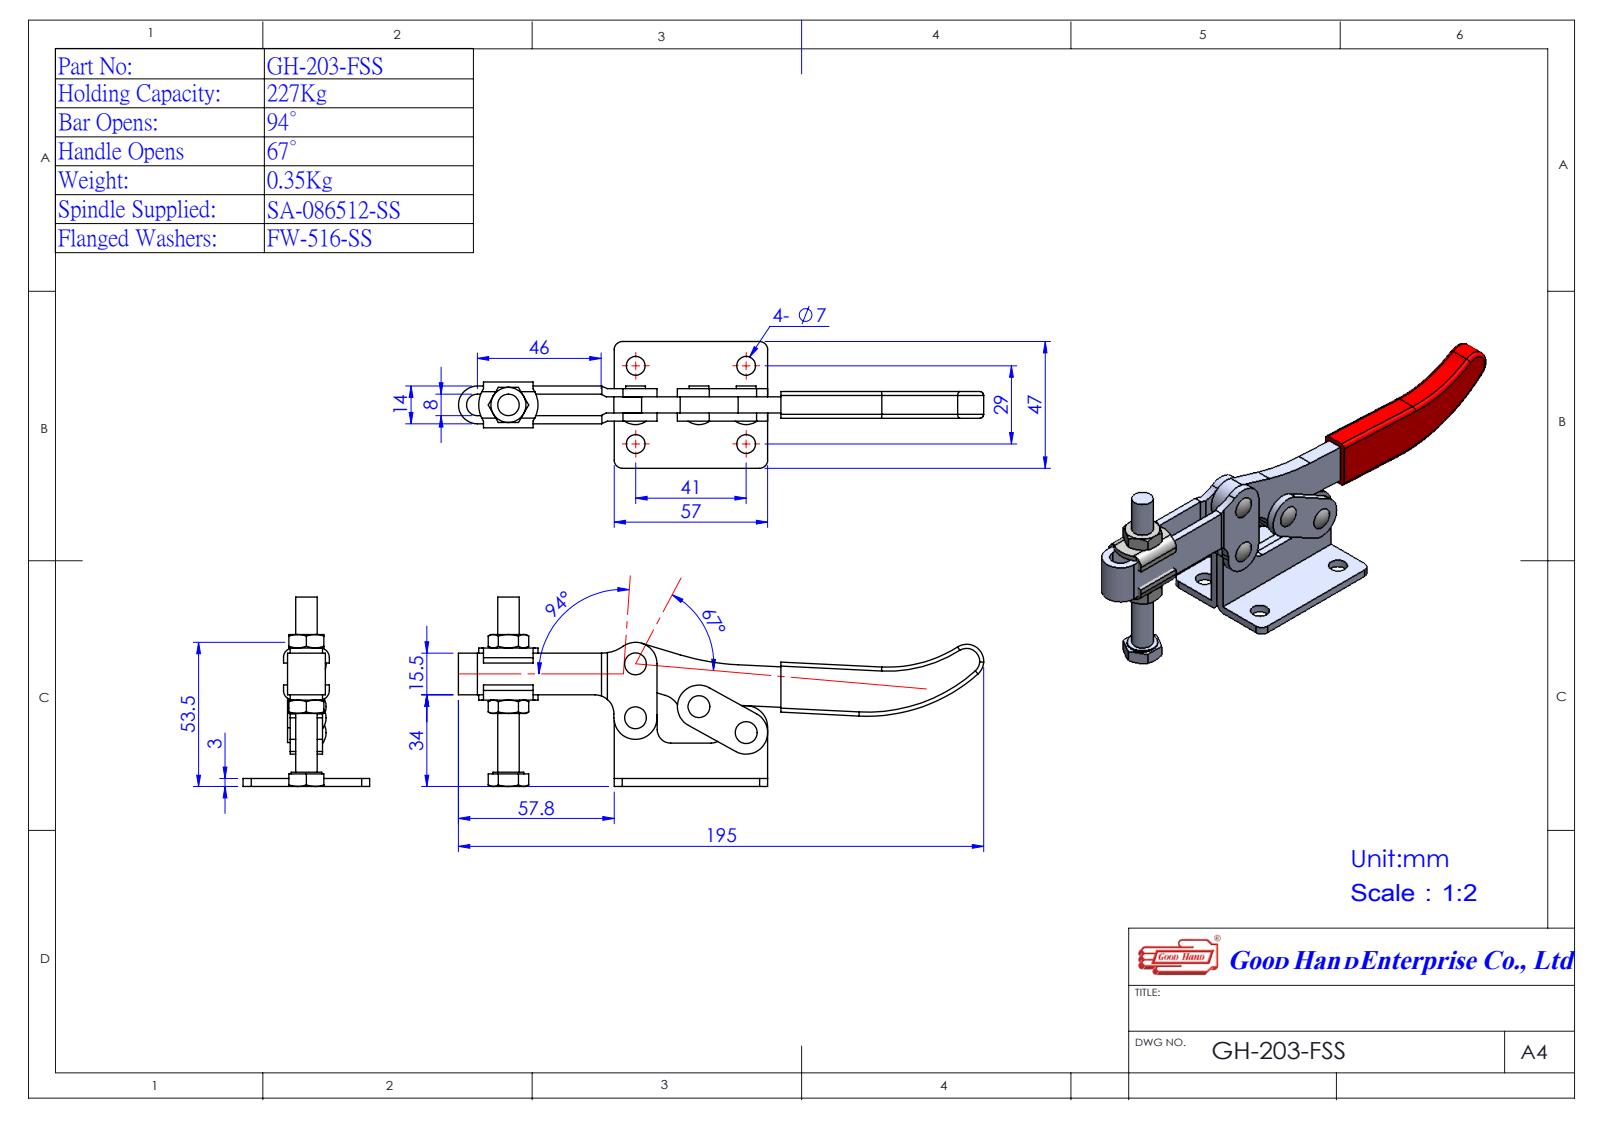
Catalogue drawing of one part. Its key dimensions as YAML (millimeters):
part_name: "GH-203-F 6.35-12; GH-203-FSS-1; 1203F01; 1203F05 (+5 more)"
step_written_by: "SolidWorks 2016 (AUTOMOTIVE_DESIGN)"
units: millimeters
bodies: {solids: 15, faces: 301, planar: 119, cylindrical: 126, other: 56}
overall_size: [195, 70.3, 47]
volume: 52419
surface_area: 34810
round_holes:
  - {diameter: 7, count: 4}
  - {diameter: 6.33, count: 3}
  - {diameter: 6.35, count: 2}
  - {diameter: 6.6, count: 1}
  - {diameter: 6.8, count: 1}
  - {diameter: 8, count: 1}
  - {diameter: 8.3, count: 1}
round_bosses_or_shafts:
  - {diameter: 7.35, count: 4}
  - {diameter: 6.35, count: 2}
  - {diameter: 11.4, count: 1}
partial_cylinders:
  - {radius: 8, count: 8}
  - {radius: 3, count: 6}
  - {radius: 1.2, count: 4}
  - {radius: 1.5, count: 4}
  - {radius: 3.6, count: 4}
  - {radius: 5, count: 2}
  - {radius: 7, count: 2}
  - {radius: 11.04, count: 2}
face_to_face_distances: [3, 1, 6, 2, 10, 9, 11, 4, 7, 8]
hole_center_spacings: [20, 29, 41, 49.43, 50.22, 89.44, 23.92, 28.4]
